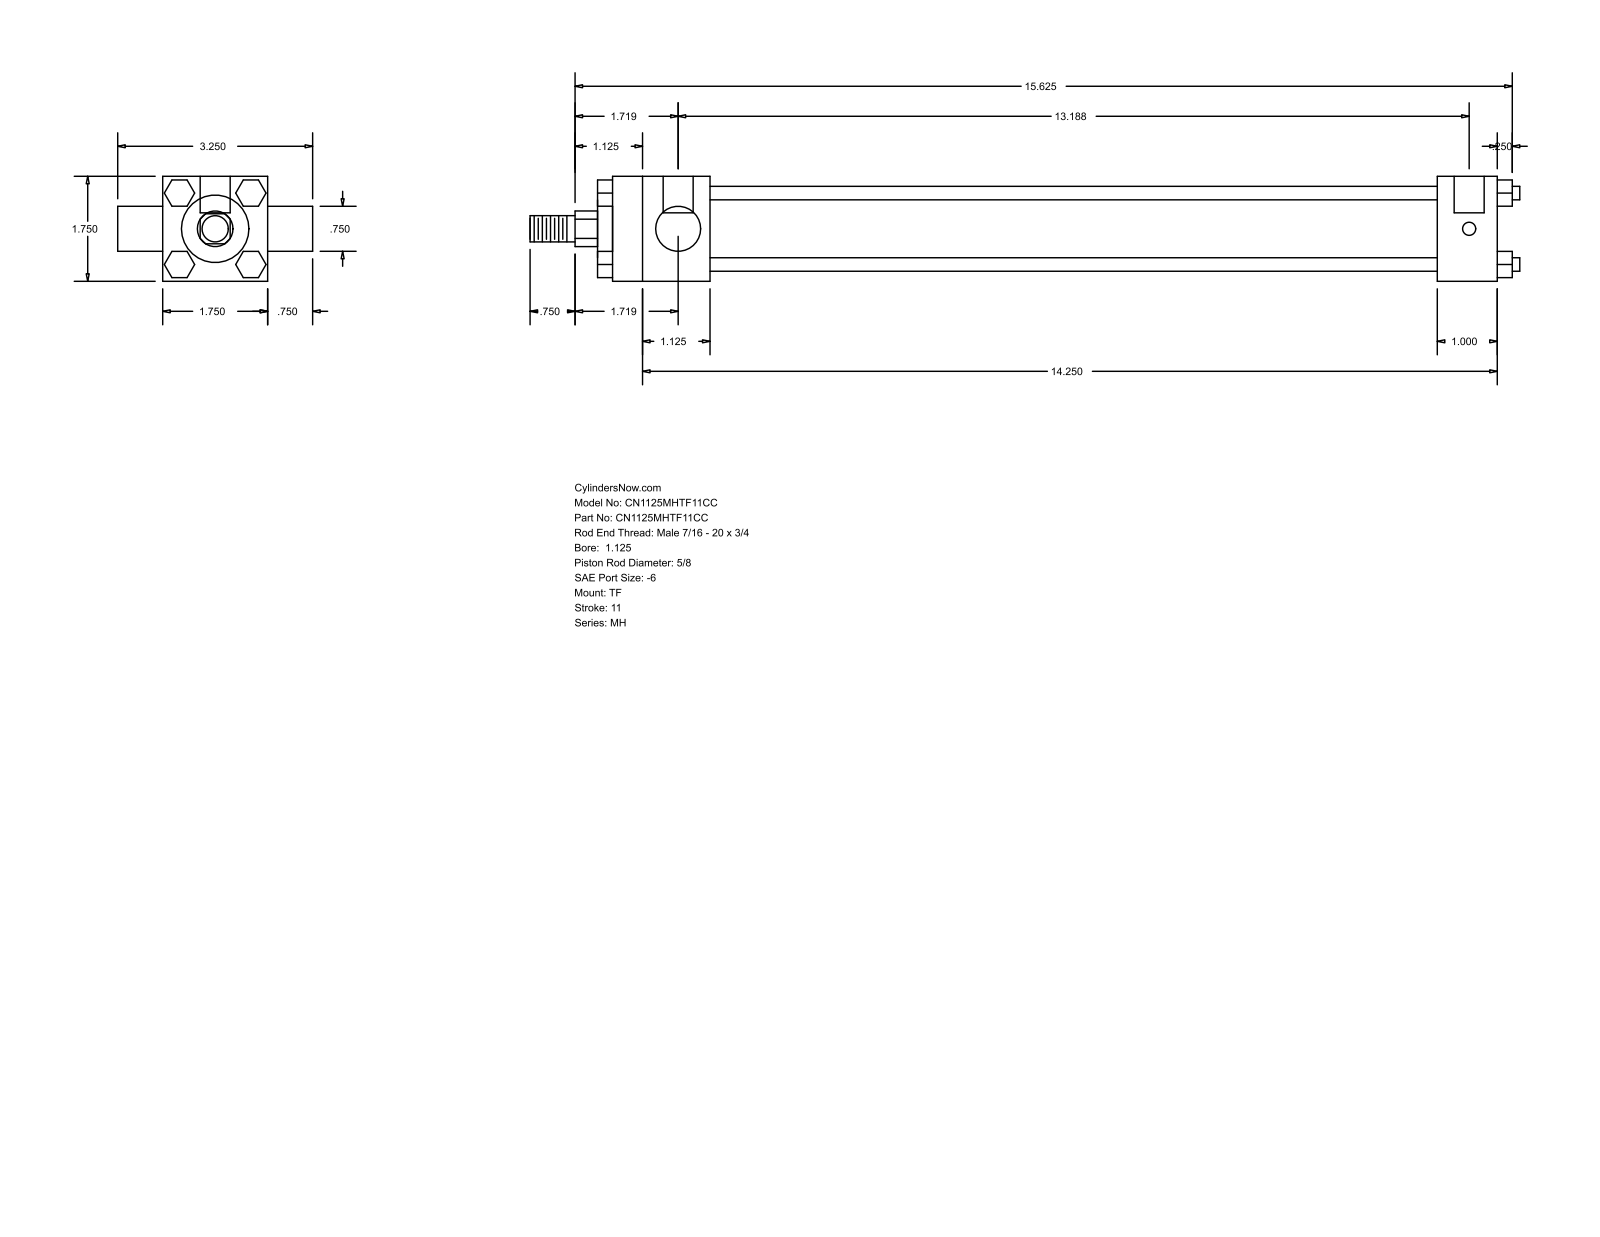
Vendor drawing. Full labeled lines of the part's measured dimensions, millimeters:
Part name (STEP PRODUCT): MH_TF__0112_0.625
STEP written by: GSSL Pune (CONFIG_CONTROL_DESIGN)
Units: millimetres
Bodies: 0 solids, 120 faces (92 planar, 28 cylindrical, 0 other)
Overall size (bounding box): 419.1 × 82.55 × 44.45
Round holes (diameter × count): ⌀5.56 ×3, ⌀12.7 ×2
Round bosses / shafts (diameter × count): ⌀5.71 ×4, ⌀34.92 ×1, ⌀28.57 ×1, ⌀19.05 ×1, ⌀15.88 ×1, ⌀11.11 ×1
Partial cylindrical surfaces — rounded edges, fillets, slot ends (radius × count): R7.54 ×1
Main face-to-face distances: 44.46, 11.11, 25.4, 307.97, 333.37, 41.27, 349.24, 374.64, 47.62, 6.35
Hole centre spacings: 3.17, 331.79, 334.96
